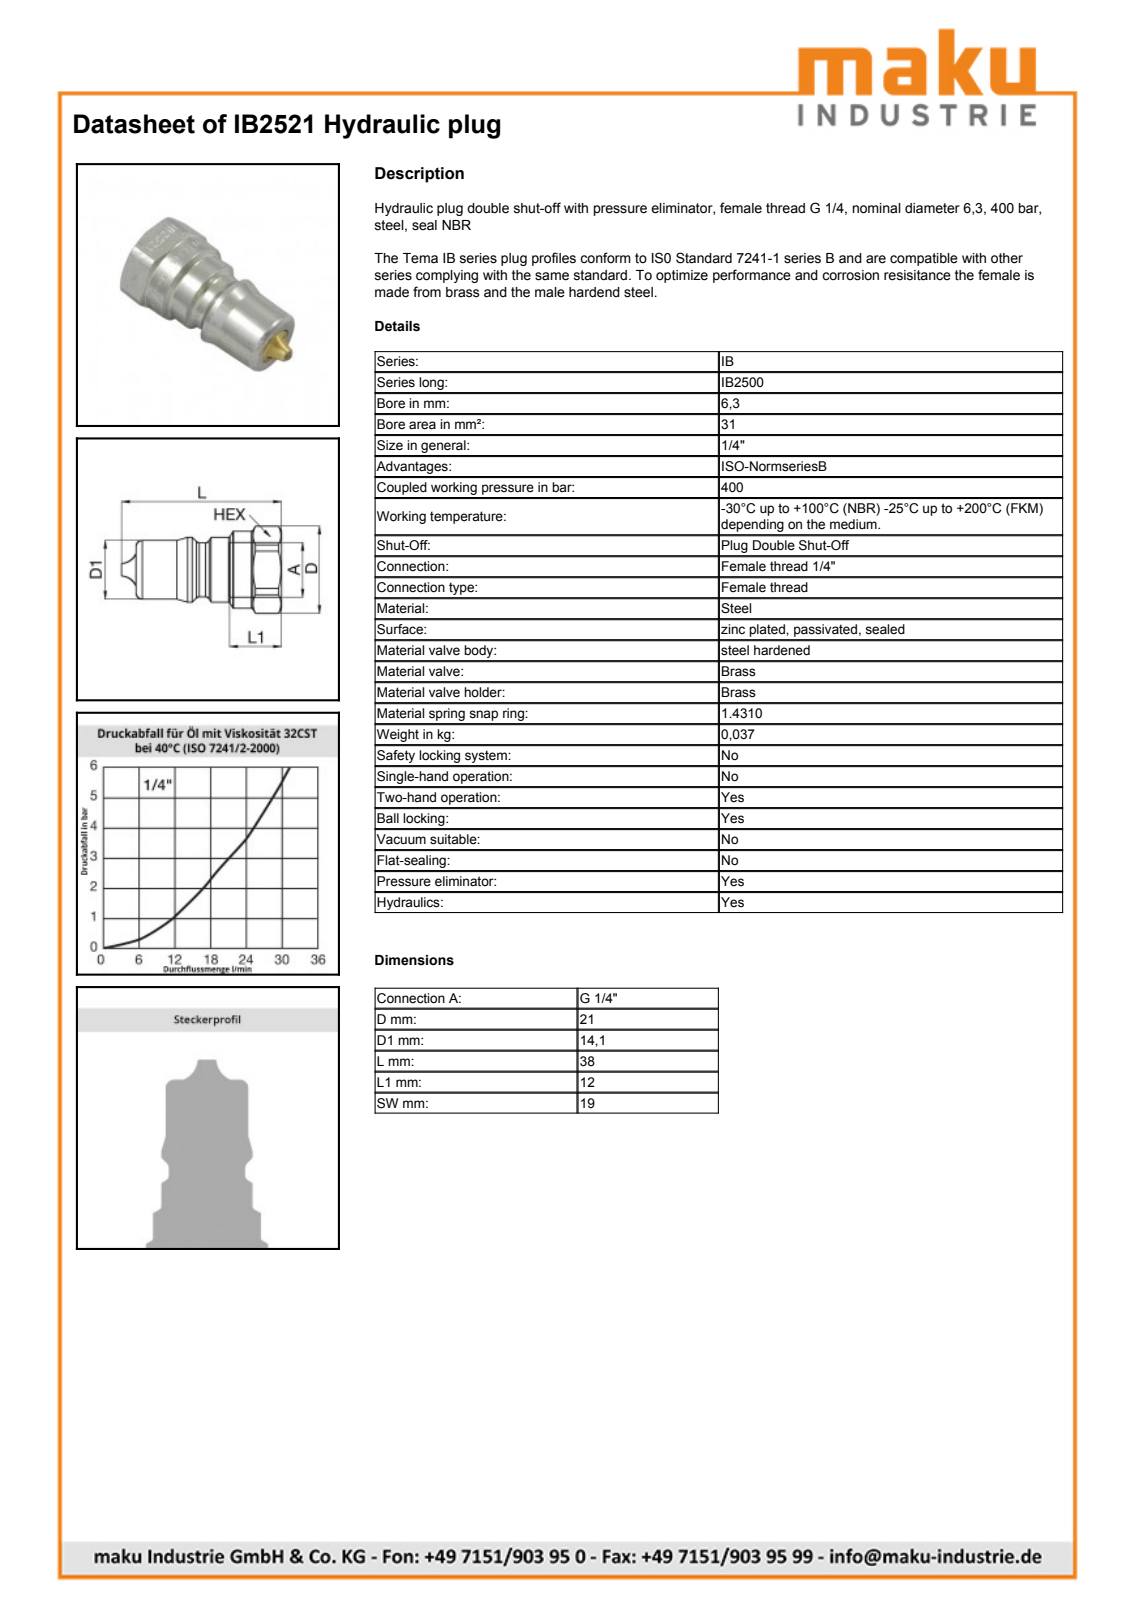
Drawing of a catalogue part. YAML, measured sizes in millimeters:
part_name: "IB2521"
step_written_by: "SolidWorks 2009 (AUTOMOTIVE_DESIGN)"
units: millimeters
bodies: {solids: 1, faces: 84, planar: 13, cylindrical: 31, other: 40}
overall_size: [38.95, 21, 19]
volume: 6164
surface_area: 2778
round_holes:
  - {diameter: 1, count: 2}
  - {diameter: 1.7, count: 1}
  - {diameter: 2.4, count: 1}
  - {diameter: 8, count: 1}
  - {diameter: 11.44, count: 1}
round_bosses_or_shafts:
  - {diameter: 18.5, count: 1}
  - {diameter: 15.6, count: 1}
  - {diameter: 14.1, count: 1}
  - {diameter: 13, count: 1}
  - {diameter: 1.5, count: 1}
partial_cylinders:
  - {radius: 10.5, count: 1}
face_to_face_distances: [19, 11.31, 35, 23.69, 38.5, 27.19, 3.5, 38.35, 27.04, 3.35]
